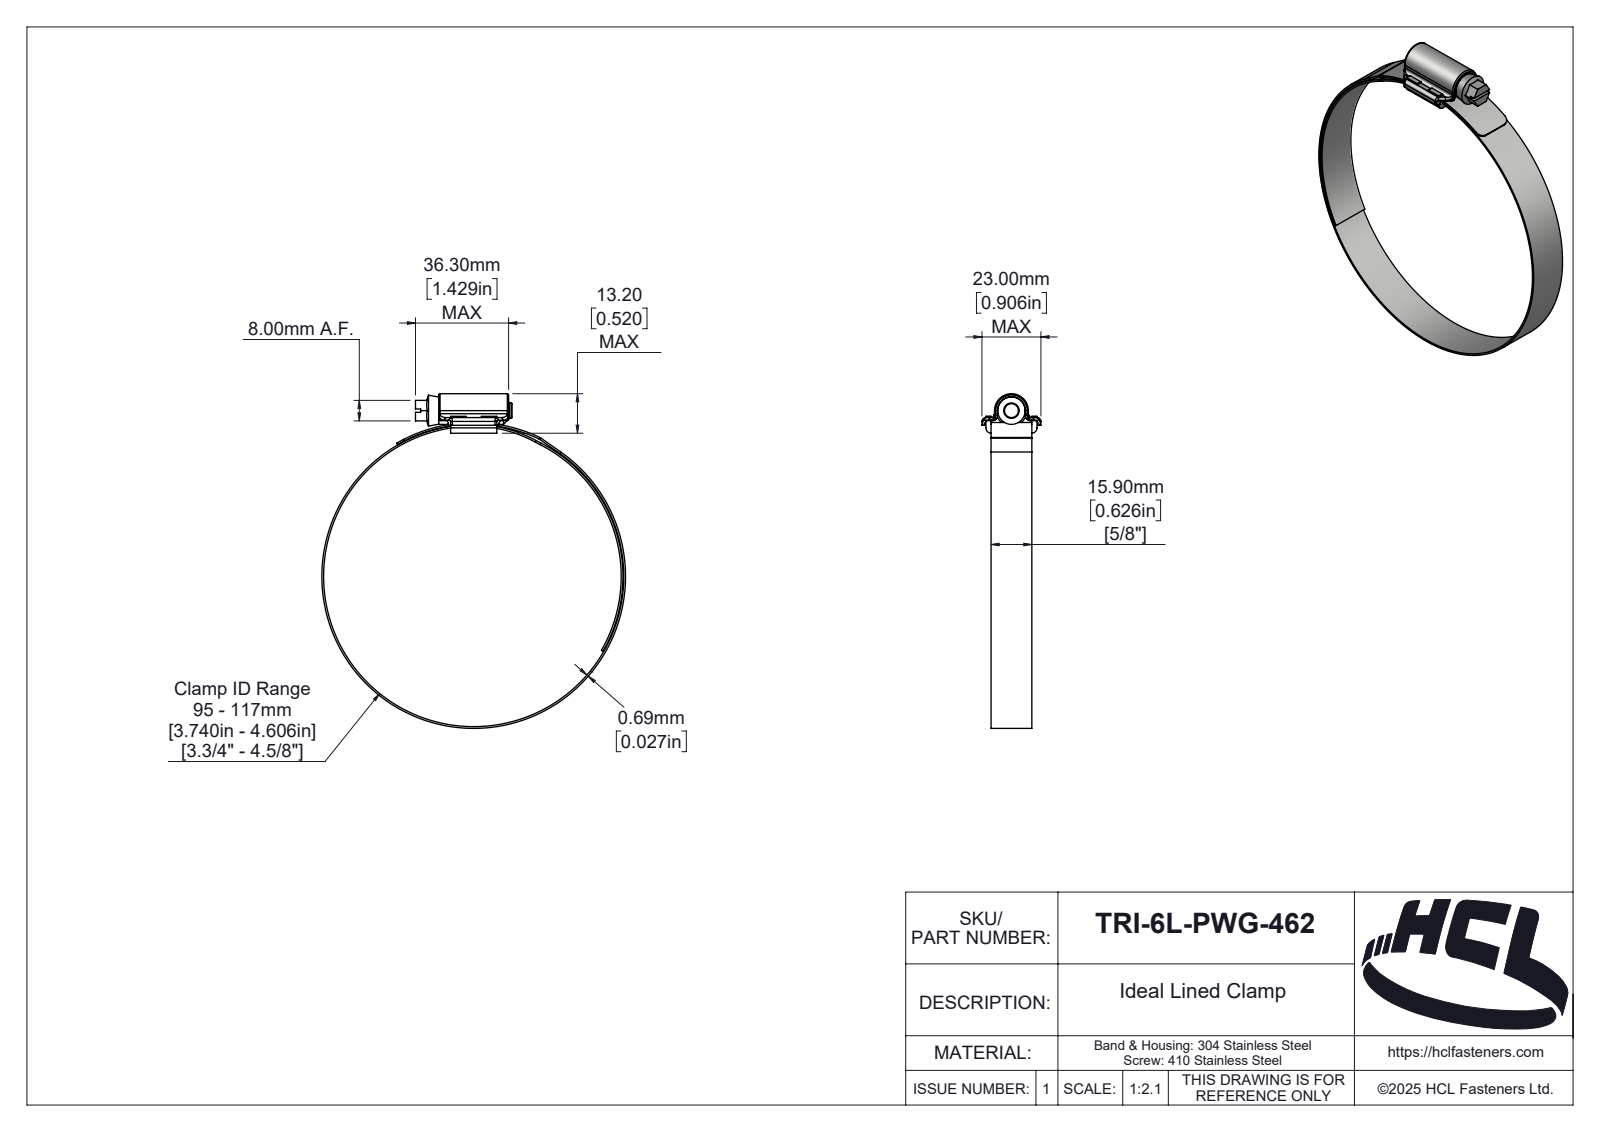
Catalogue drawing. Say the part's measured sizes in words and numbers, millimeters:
The part is named "TRI-6L-PWG-462". Its 3-D file was written by "SolidWorks 2025 (AUTOMOTIVE_DESIGN)". It is 4 solids with 268 faces: 87 planar, 102 cylindrical and 79 other. Overall it measures 130.39 by 118.38 by 23 millimeters. Its volume is 10 928 cubic millimeters and its surface area 21 949 square millimeters. Round holes: 1 of diameter 117. Round bosses or shafts: 1 of diameter 118.38, 1 of diameter 10.7, 1 of diameter 6. Partial cylindrical surfaces (rounded edges, fillets, slot ends): 14 of radius 1, 4 of radius 0.5, 4 of radius 1.5, 3 of radius 2, 2 of radius 0.1, 2 of radius 2.1, 2 of radius 3, 1 of radius 0.46. The main face-to-face distances are 2, 15.9, 17.9, 4.9, 0.69, 1.2, 4.55, 3.35, 15.35, 2.55.
